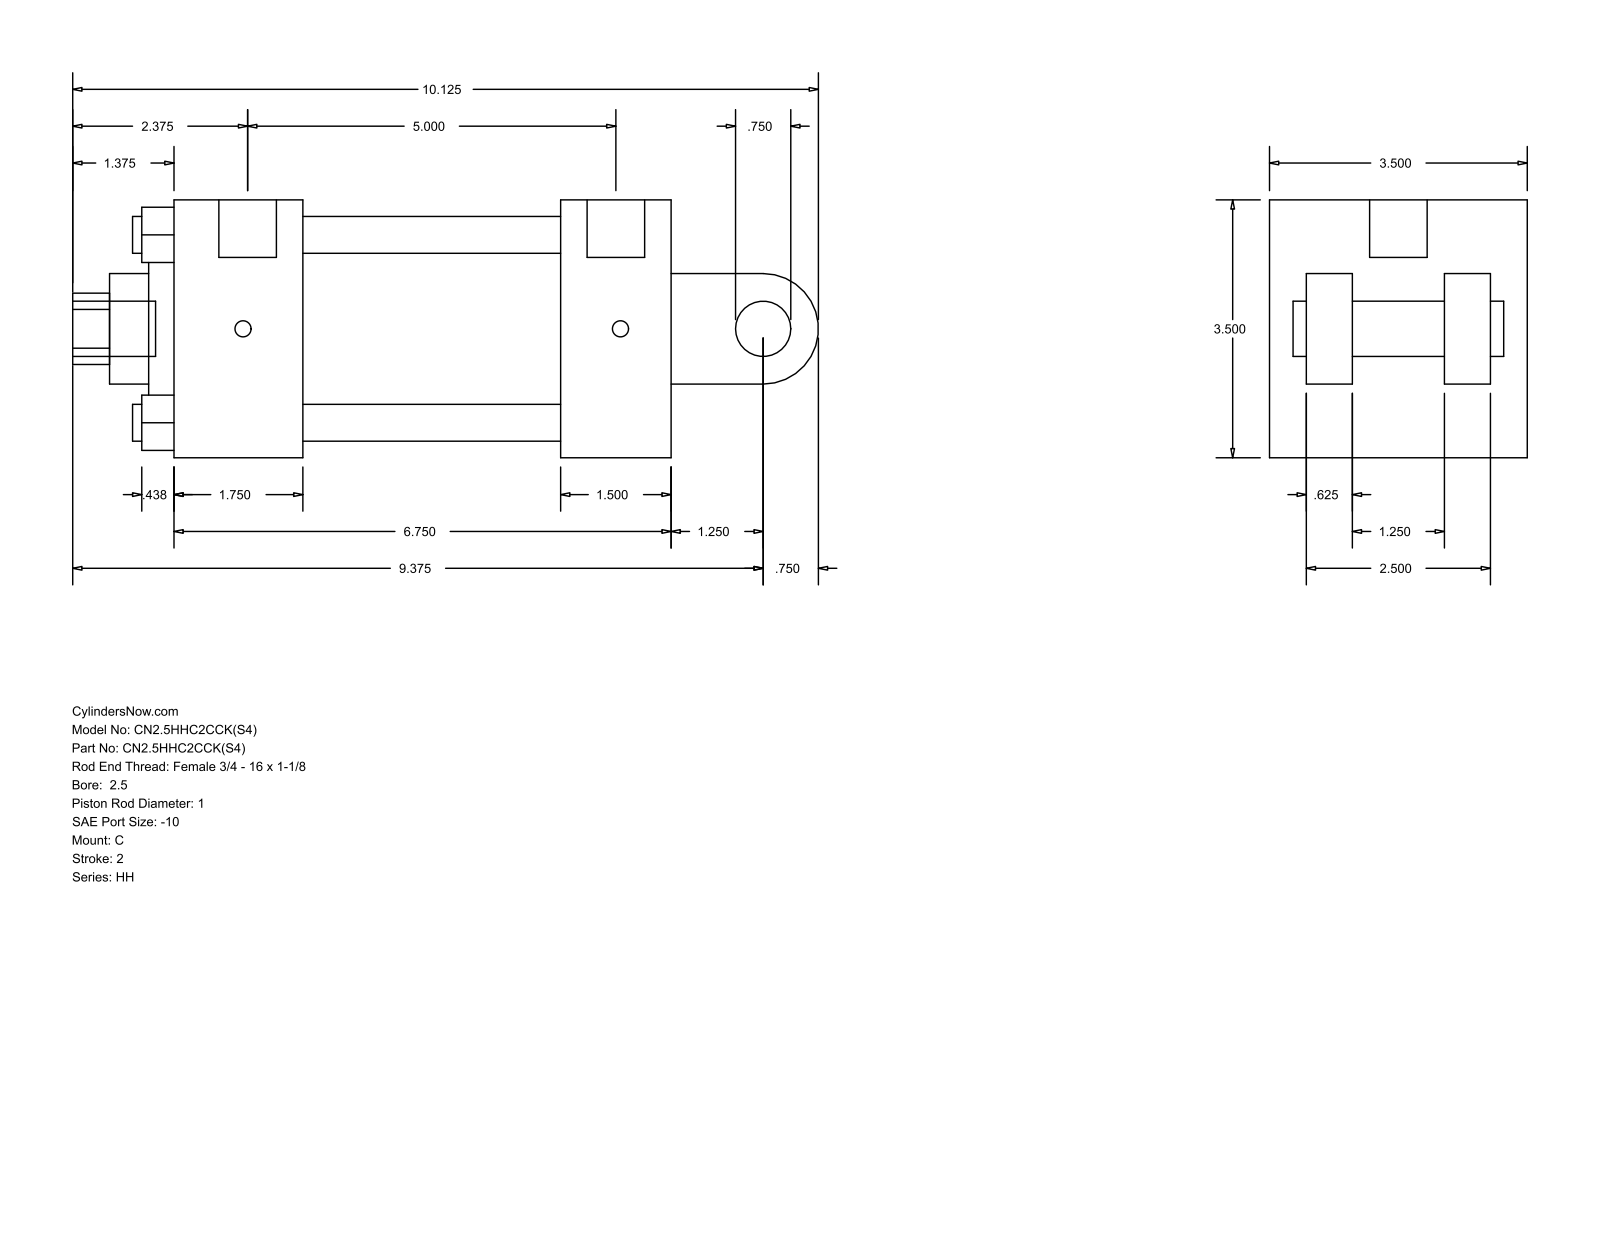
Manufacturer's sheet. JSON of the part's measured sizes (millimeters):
{"part_name": "HH_C__0250_1", "step_written_by": "GSSL Pune (CONFIG_CONTROL_DESIGN)", "units": "millimeters", "bodies": {"solids": 0, "faces": 101, "planar": 71, "cylindrical": 30, "other": 0}, "overall_size": [257.18, 88.9, 88.9], "round_holes": [[12.7, 4], [5.56, 2], [19.84, 1], [25.4, 1], [38.1, 1], [60.33, 1], [73.03, 1]], "round_bosses_or_shafts": [[19.05, 2], [5.56, 2], [19.84, 1]], "partial_cylinders_radius": [[12.29, 1], [19.05, 1]], "face_to_face_distances": [88.9, 38.1, 171.46, 63.5, 15.87, 133.36, 44.46, 127, 12.7, 28.57], "hole_center_spacings": [45.79, 64.76, 91.58, 1.59]}
